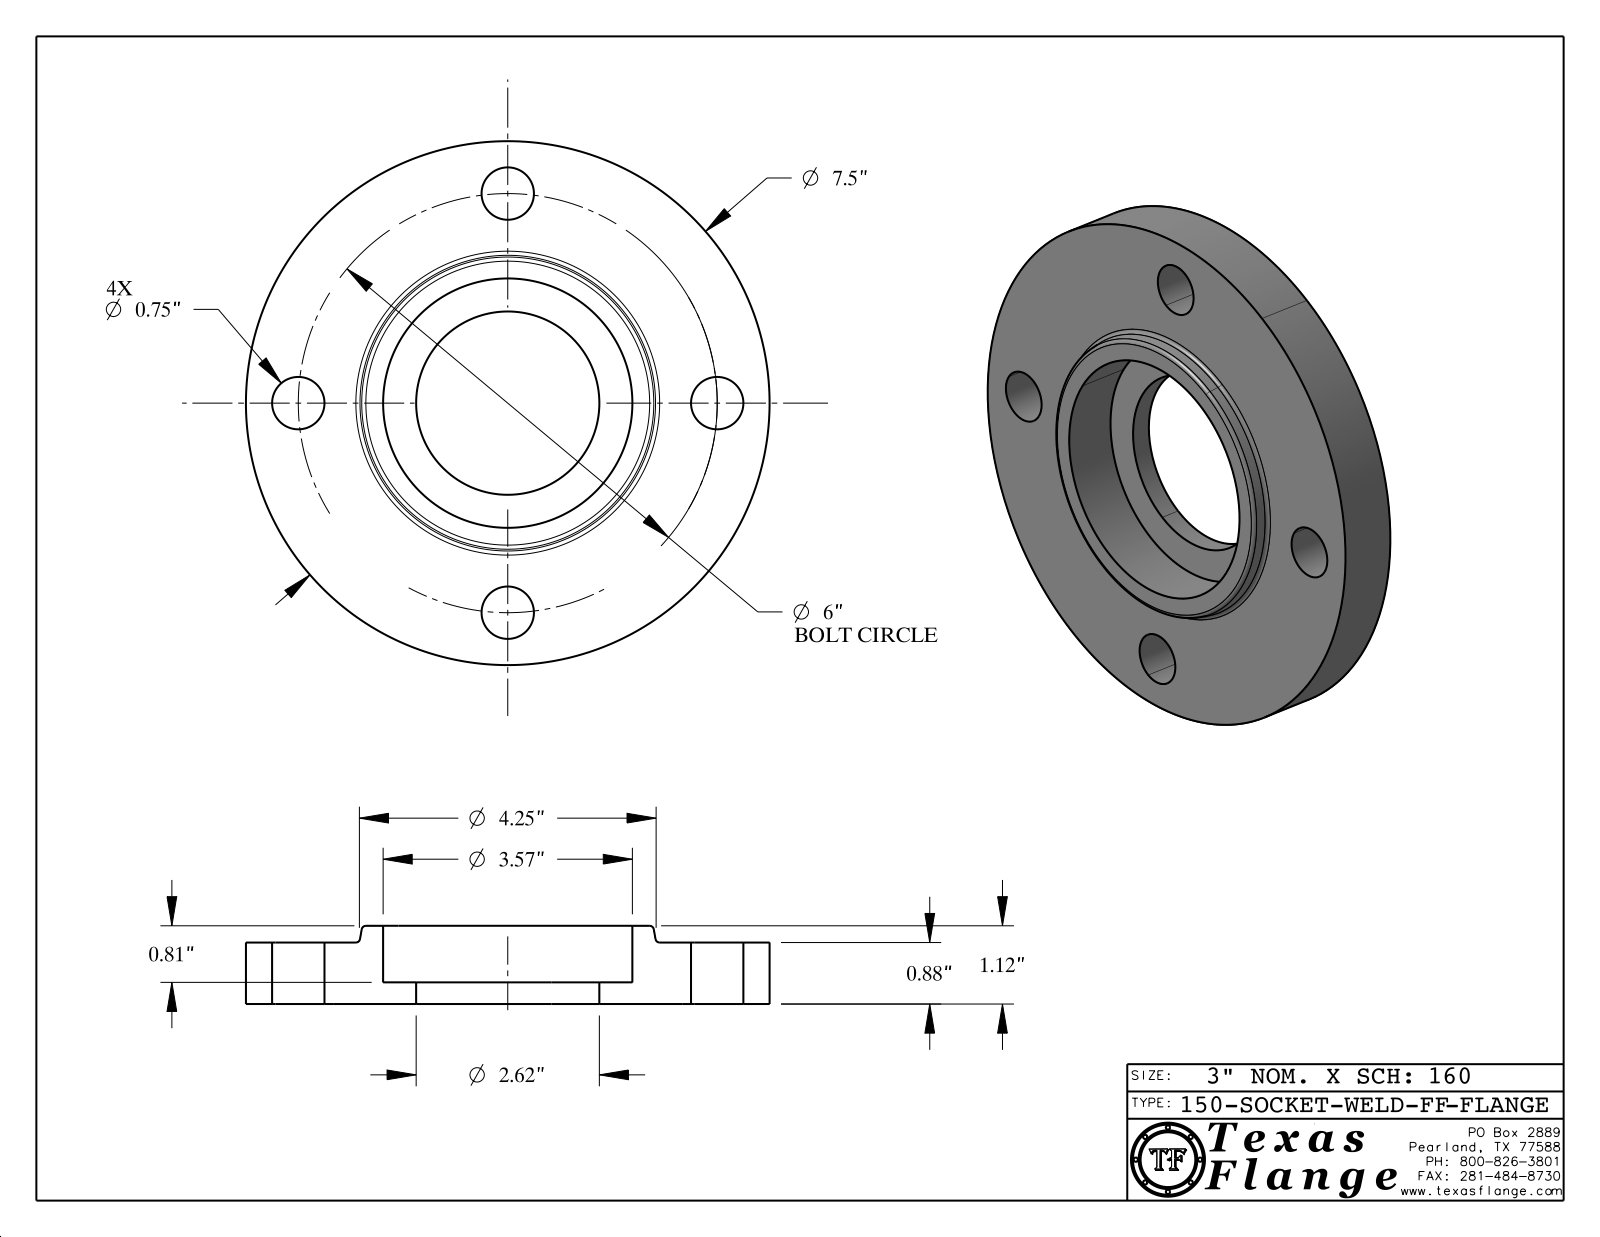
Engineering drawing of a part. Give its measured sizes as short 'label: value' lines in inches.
name: 150-SOCKET-WELD-FF
written by: CATIA V5 STEP AP214 (AUTOMOTIVE_DESIGN)
unit: in
bodies: 1 solid, 410 faces (370 planar, 34 cylindrical, 6 other)
size: 7.5 × 7.5 × 1.12
volume: 30.87 in³; area: 117 in²
holes: 4× ⌀0.75, 1× ⌀0.495, 1× ⌀2.624, 1× ⌀3.57
bosses: 8× ⌀0.03, 1× ⌀7.5, 1× ⌀0.39
face distances: 0.88, 0.31, 0.57, 1.12, 0.81, 0.24, 0.865, 0.555, 0.015, 0.255
hole spacings: 3, 4.243, 2.296, 5.543, 6
